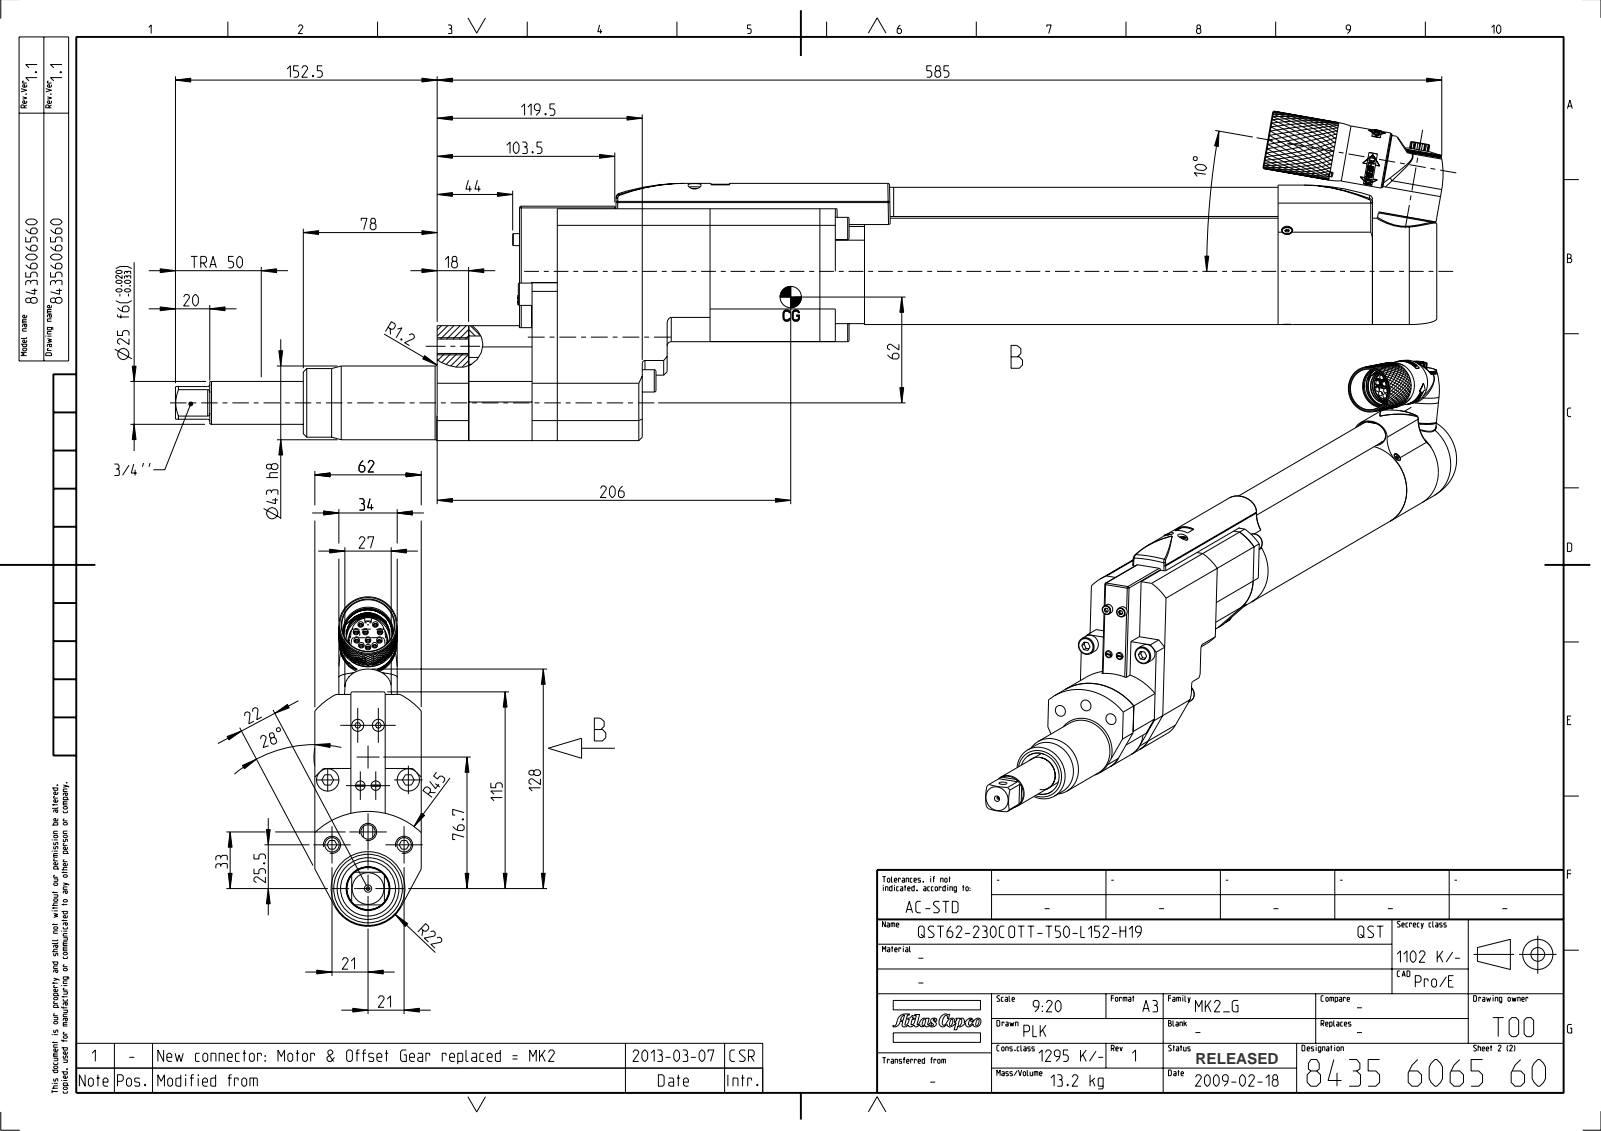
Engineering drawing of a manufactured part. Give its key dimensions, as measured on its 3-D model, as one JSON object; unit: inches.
{"part_name": "8435606560_ASM_SW0001", "step_written_by": "CREO PARAMETRIC BY PTC INC, 2022414 (AP242_MANAGED_MODEL_BASED_3D_ENGINEERING_MIM_LF)", "units": "inches", "bodies": {"solids": 1, "faces": 1539, "planar": 739, "cylindrical": 354, "other": 446}, "overall_size": [29.08, 7.561, 2.461], "volume_in3": 146, "surface_area_in2": 402.3, "round_holes": [[0.128, 4], [0.177, 4], [0.433, 4], [0.256, 3], [0.33, 3], [0.097, 2], [0.115, 2], [0.13, 2], [0.194, 2], [0.252, 2], [0.262, 2], [0.079, 1]], "round_bosses_or_shafts": [[0.512, 7], [0.276, 4], [0.157, 4], [1.339, 3], [0.236, 3], [0.118, 3], [0.22, 2], [2.441, 1]], "partial_cylinders_radius": [[0.011, 12], [0.02, 12], [0.039, 10], [0.02, 4], [0.047, 4], [0.906, 4], [0.276, 3], [0.016, 2]], "face_to_face_distances": [2.441, 0.827, 0.039, 0.866, 1.614, 0.748, 1.575, 0.217, 20.176, 20.754], "hole_center_spacings": [0.472, 1.85, 0.508, 0.509, 0.63, 0.787, 0.878, 0.898]}
